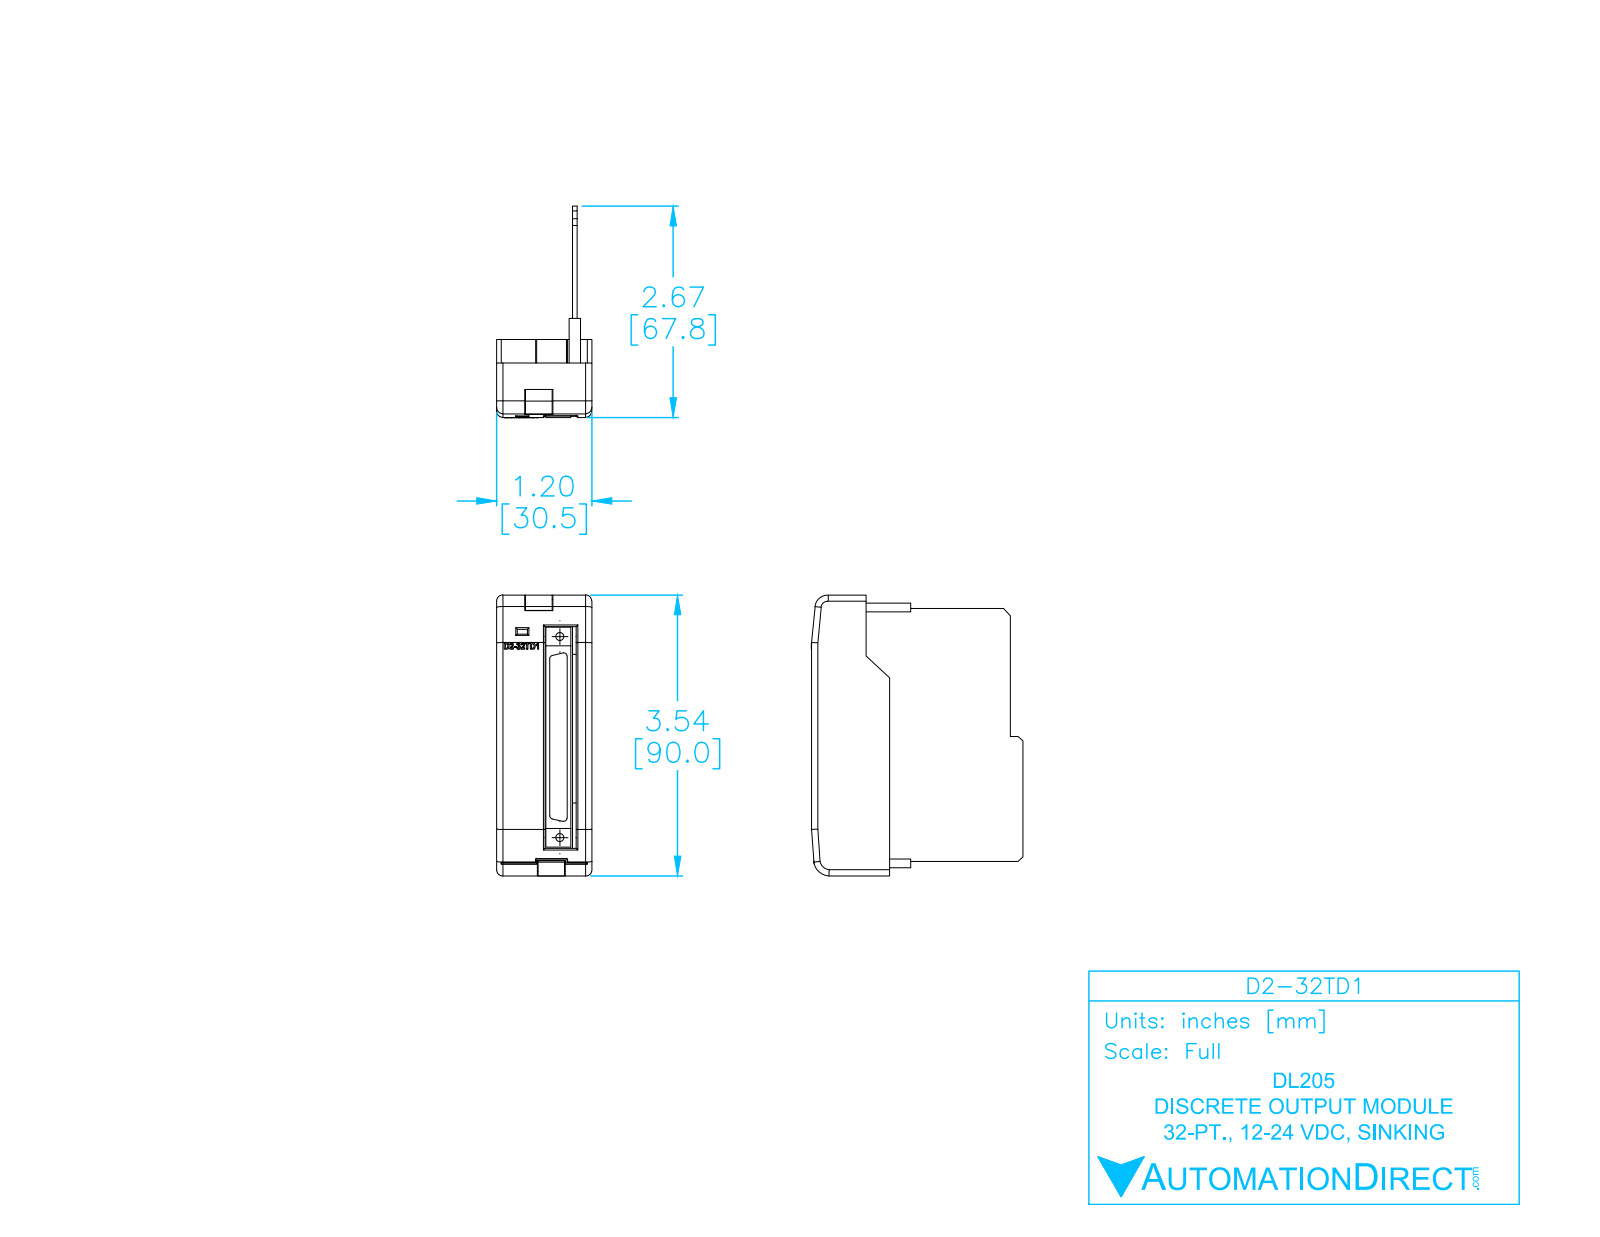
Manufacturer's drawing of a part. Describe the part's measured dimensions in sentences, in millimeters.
The part is named "D2-32TD1". Its 3-D file was written by "SolidWorks 2009 (AUTOMOTIVE_DESIGN)". It is 5 solids with 319 faces: 192 planar, 63 cylindrical and 64 other. Overall it measures 90 by 67.85 by 30.5 millimeters. Its volume is 20 870 cubic millimeters and its surface area 29 166 square millimeters. Round holes: 2 of diameter 2.5. Partial cylindrical surfaces (rounded edges, fillets, slot ends): 24 of radius 0.5, 10 of radius 2, 4 of radius 0.25, 4 of radius 1, 1 of radius 2.62, 1 of radius 3.79, 1 of radius 4.12, 1 of radius 5.29. The main face-to-face distances are 1.5, 4.72, 3.22, 6.22, 24.28, 29, 0.5, 25.78, 30.5, 22.78. The hole center spacings are 64.38.
